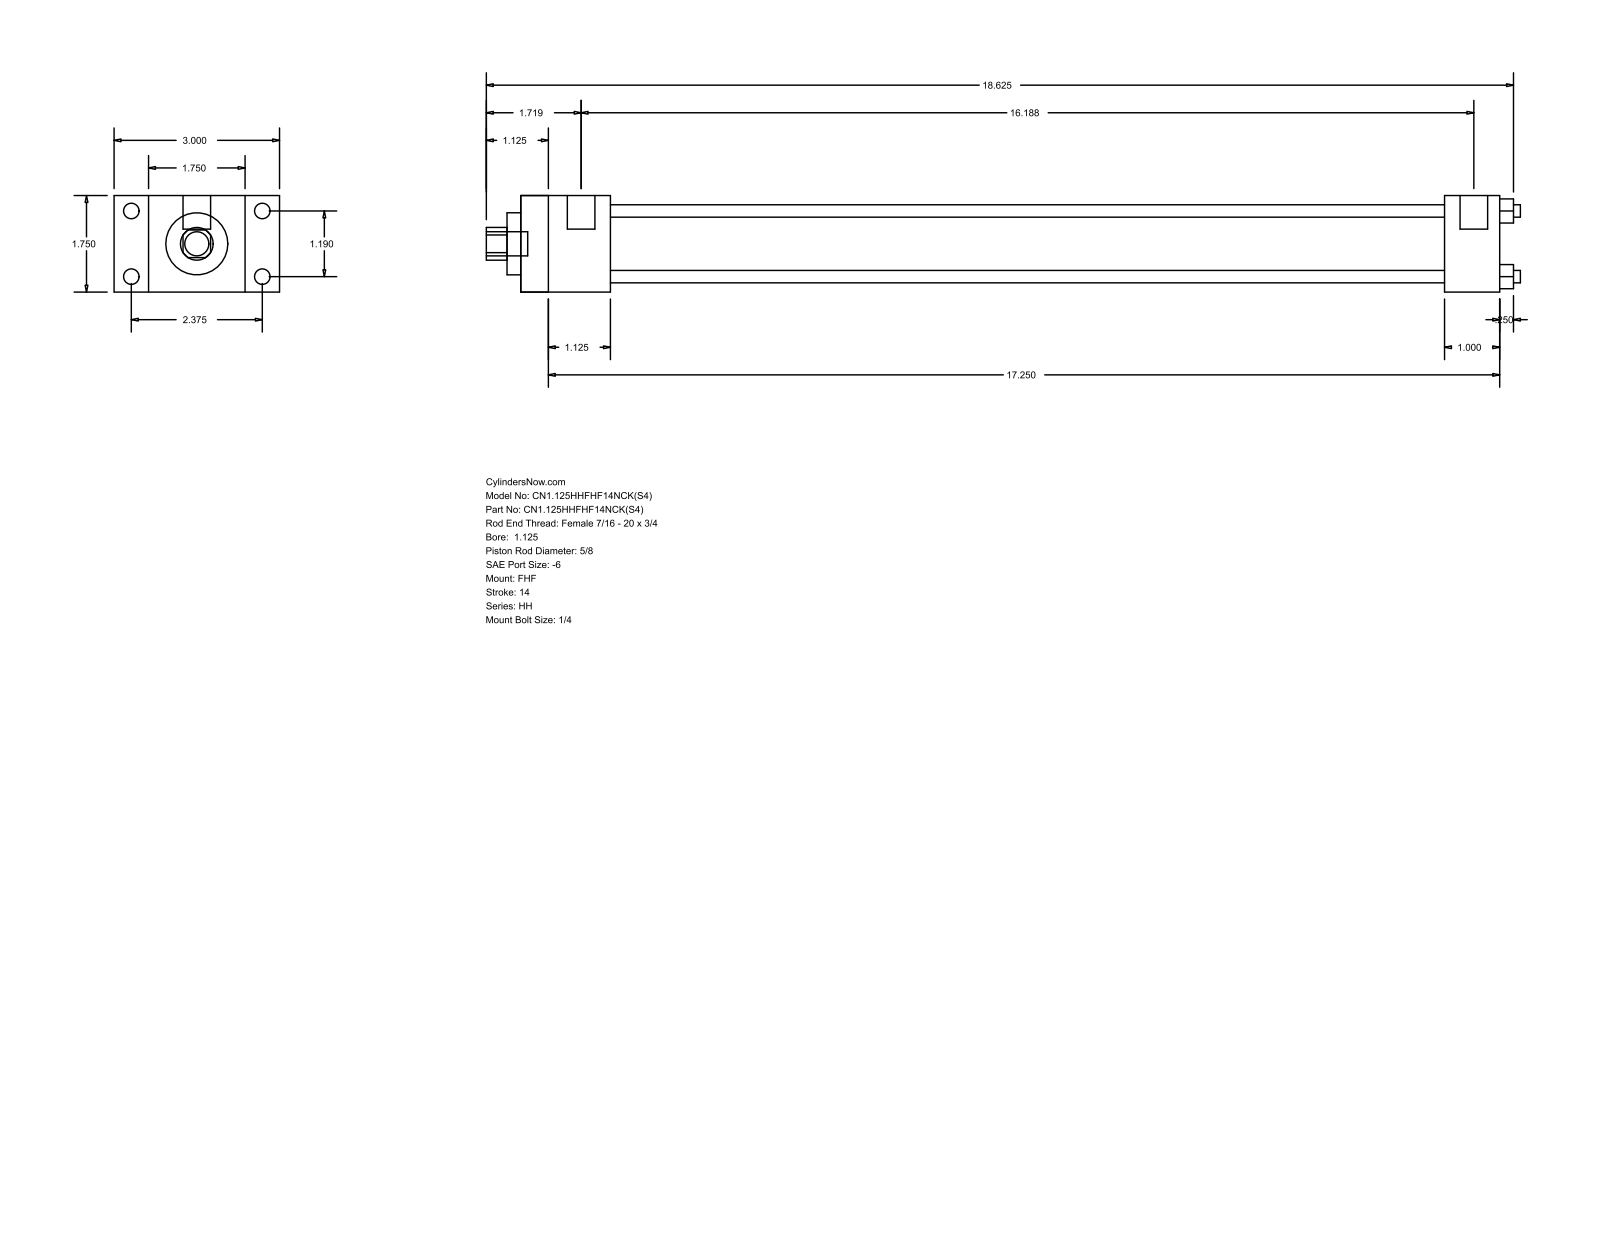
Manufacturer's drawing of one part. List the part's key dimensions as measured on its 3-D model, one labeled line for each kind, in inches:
Part name (STEP PRODUCT): HH_FHF__0112_0.625
STEP written by: GSSL Pune (CONFIG_CONTROL_DESIGN)
Units: inches
Bodies: 0 solids, 88 faces (60 planar, 28 cylindrical, 0 other)
Overall size (bounding box): 18.75 × 3 × 1.75
Round holes (diameter × count): ⌀0.225 ×4, ⌀0.625 ×1, ⌀1.125 ×1, ⌀1.375 ×1
Round bosses / shafts (diameter × count): ⌀0.281 ×4, ⌀0.219 ×4, ⌀0.5 ×2, ⌀0.437 ×1
Partial cylindrical surfaces — rounded edges, fillets, slot ends (radius × count): R0.297 ×1
Main face-to-face distances: 1.75, 0.625, 2.375, 1.625, 3, 17.75, 16.125, 16.75, 15.125, 1
Hole centre spacings: 0.841, 1.19, 1.683
